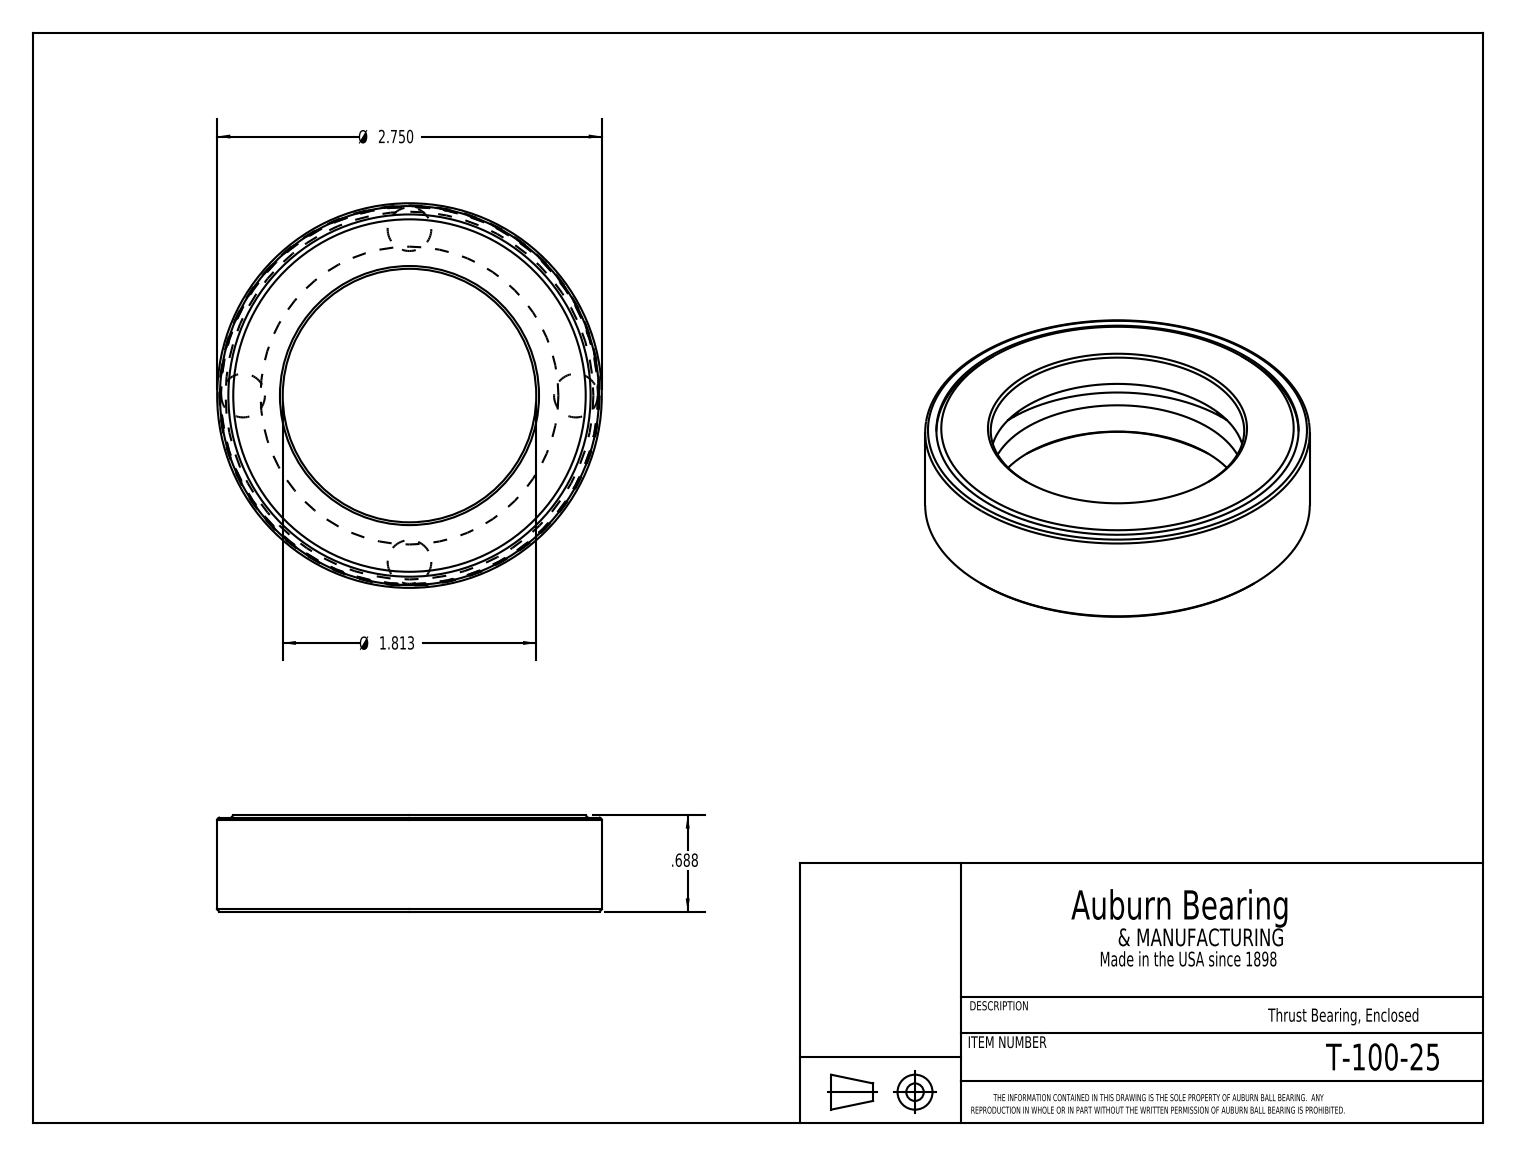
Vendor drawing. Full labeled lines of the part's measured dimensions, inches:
Part name (STEP PRODUCT): T-100-25
STEP written by: SolidWorks 2016 (CONFIG_CONTROL_DESIGN)
Units: inches
Bodies: 6 solids, 28 faces (9 planar, 7 cylindrical, 12 other)
Overall size (bounding box): 2.75 × 2.75 × 0.688
Volume: 1.569 in³ · Surface area: 29.49 in²
Round holes (diameter × count): ⌀1.813 ×1, ⌀2.59 ×1, ⌀2.71 ×1
Round bosses / shafts (diameter × count): ⌀2.75 ×1, ⌀2.696 ×1
Main face-to-face distances: 0.25, 0.437, 0.687, 0.187, 0.672, 0.422, 0.235, 0.015, 0.652, 0.402
